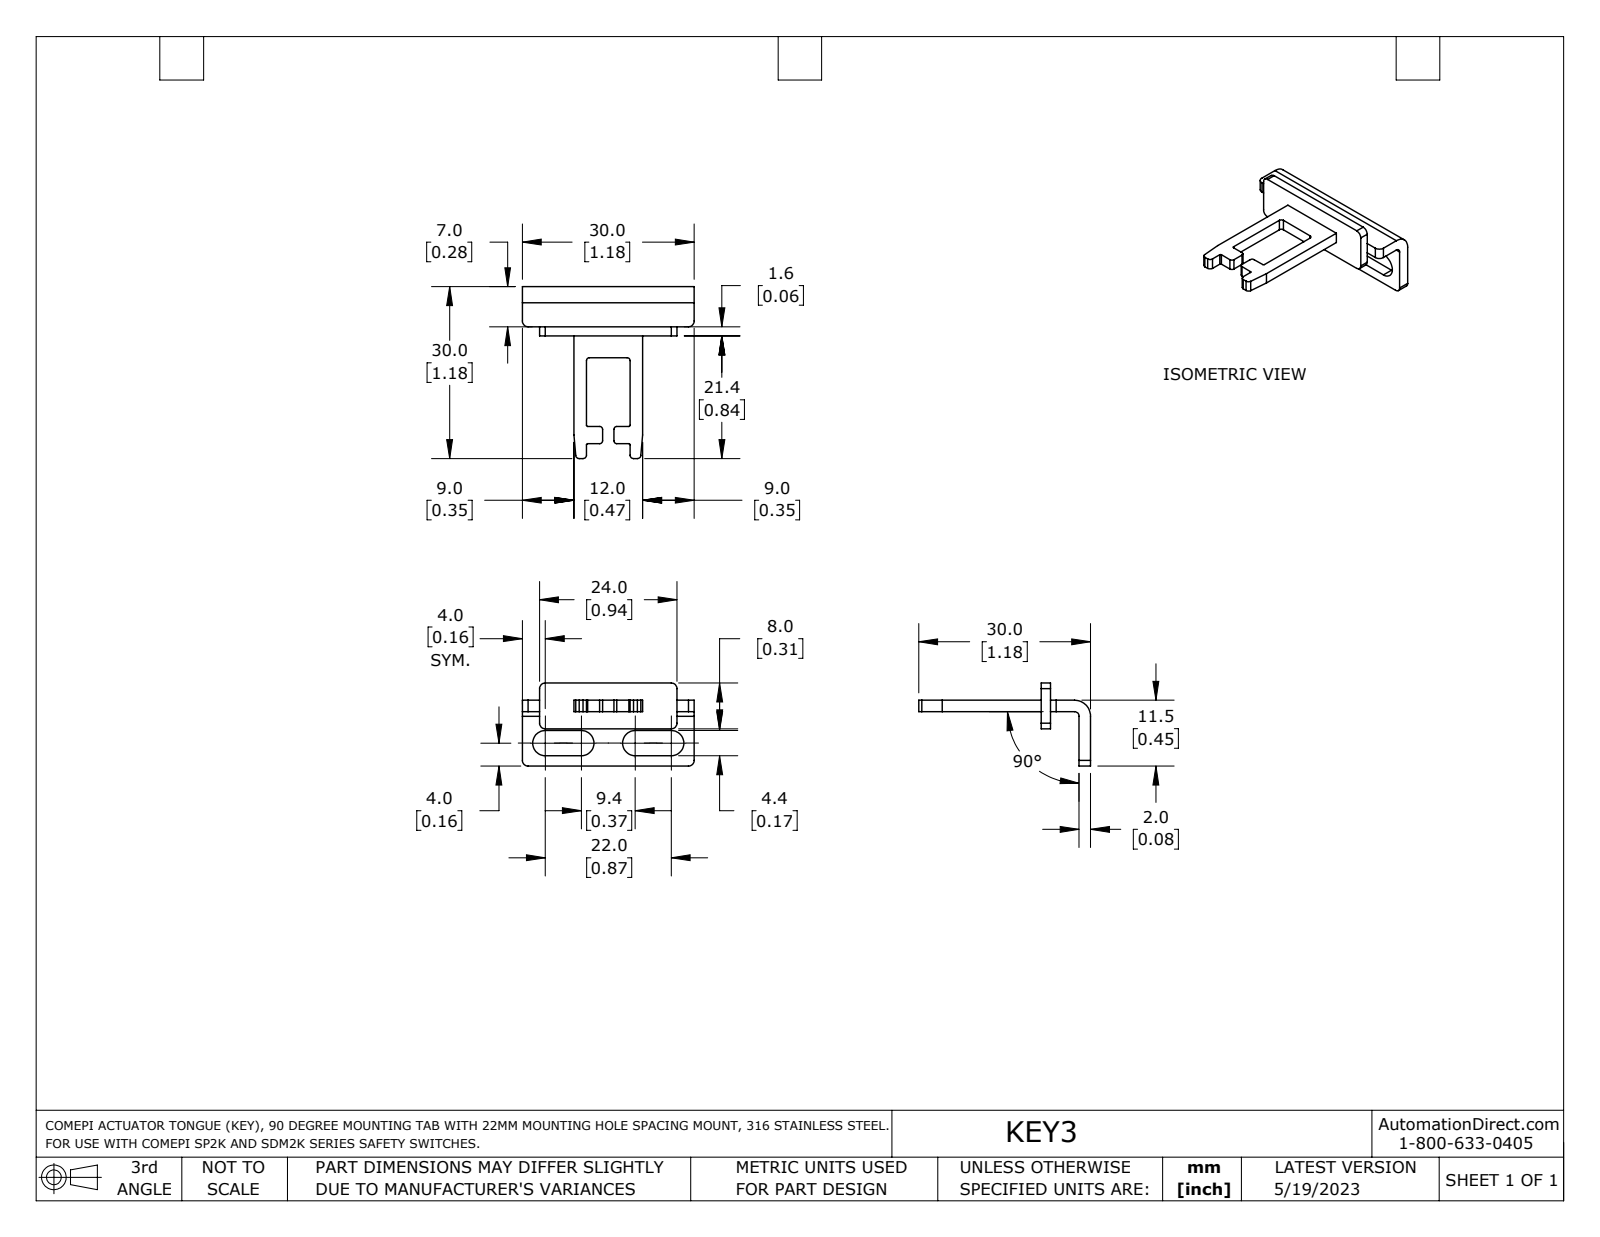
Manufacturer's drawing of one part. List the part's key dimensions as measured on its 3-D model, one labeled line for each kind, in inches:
Part name (STEP PRODUCT): KEY3
STEP written by: SolidWorks 2021 (AUTOMOTIVE_DESIGN)
Units: inches
Bodies: 1 solid, 67 faces (39 planar, 28 cylindrical, 0 other)
Overall size (bounding box): 1.181 × 1.181 × 0.571
Volume: 0.083 in³ · Surface area: 2.928 in²
Partial cylindrical surfaces — rounded edges, fillets, slot ends (radius × count): R0.039 ×8, R0.02 ×6, R0.008 ×4, R0.024 ×4, R0.087 ×4, R0.031 ×1, R0.11 ×1
Main face-to-face distances: 0.079, 0.197, 0.339, 0.26, 0.276, 0.063, 0.118, 0.74, 0.374, 0.453
